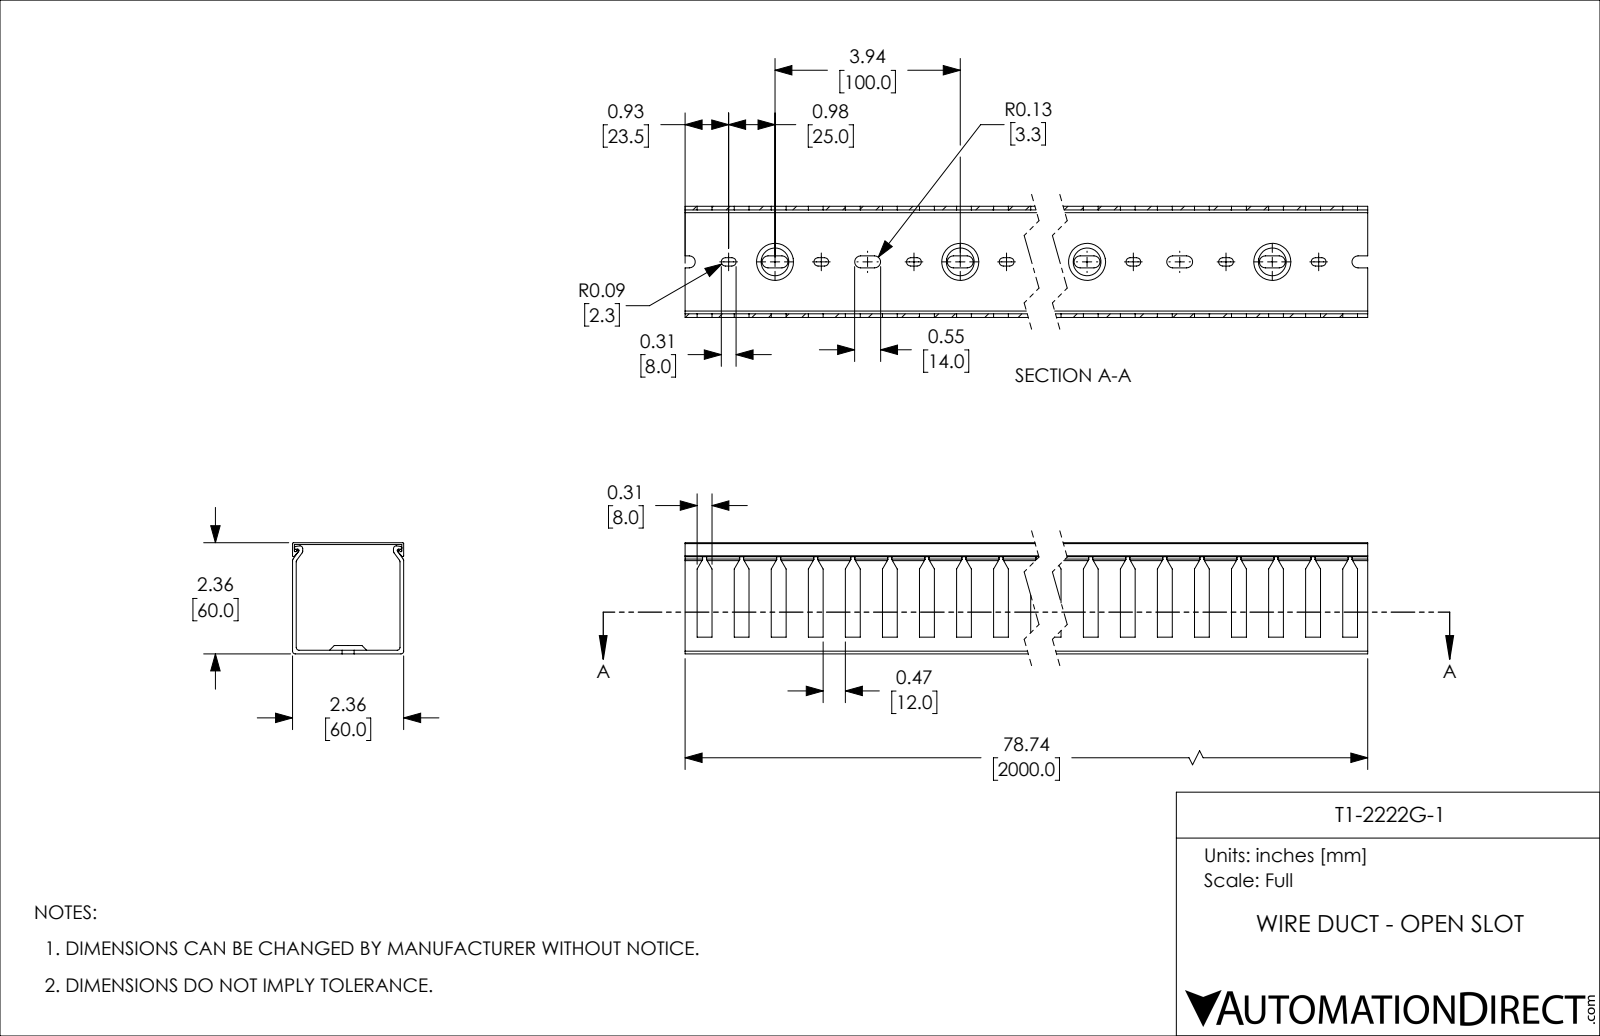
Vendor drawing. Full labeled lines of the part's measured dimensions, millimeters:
Part name (STEP PRODUCT): T1-2222G-1
STEP written by: SolidWorks 2021 (CONFIG_CONTROL_DESIGN)
Units: millimetres
Bodies: 2 solids, 1005 faces (534 planar, 431 cylindrical, 40 other)
Overall size (bounding box): 2000 × 60 × 60
Volume: 854 712 mm³ · Surface area: 1 012 000 mm²
Partial cylindrical surfaces — rounded edges, fillets, slot ends (radius × count): R2.25 ×80, R3.25 ×80, R1.5 ×12, R0.5 ×8, R0.75 ×6
Main face-to-face distances: 2, 58, 60, 1, 59, 57, 56, 4.5, 54.5, 5.5
